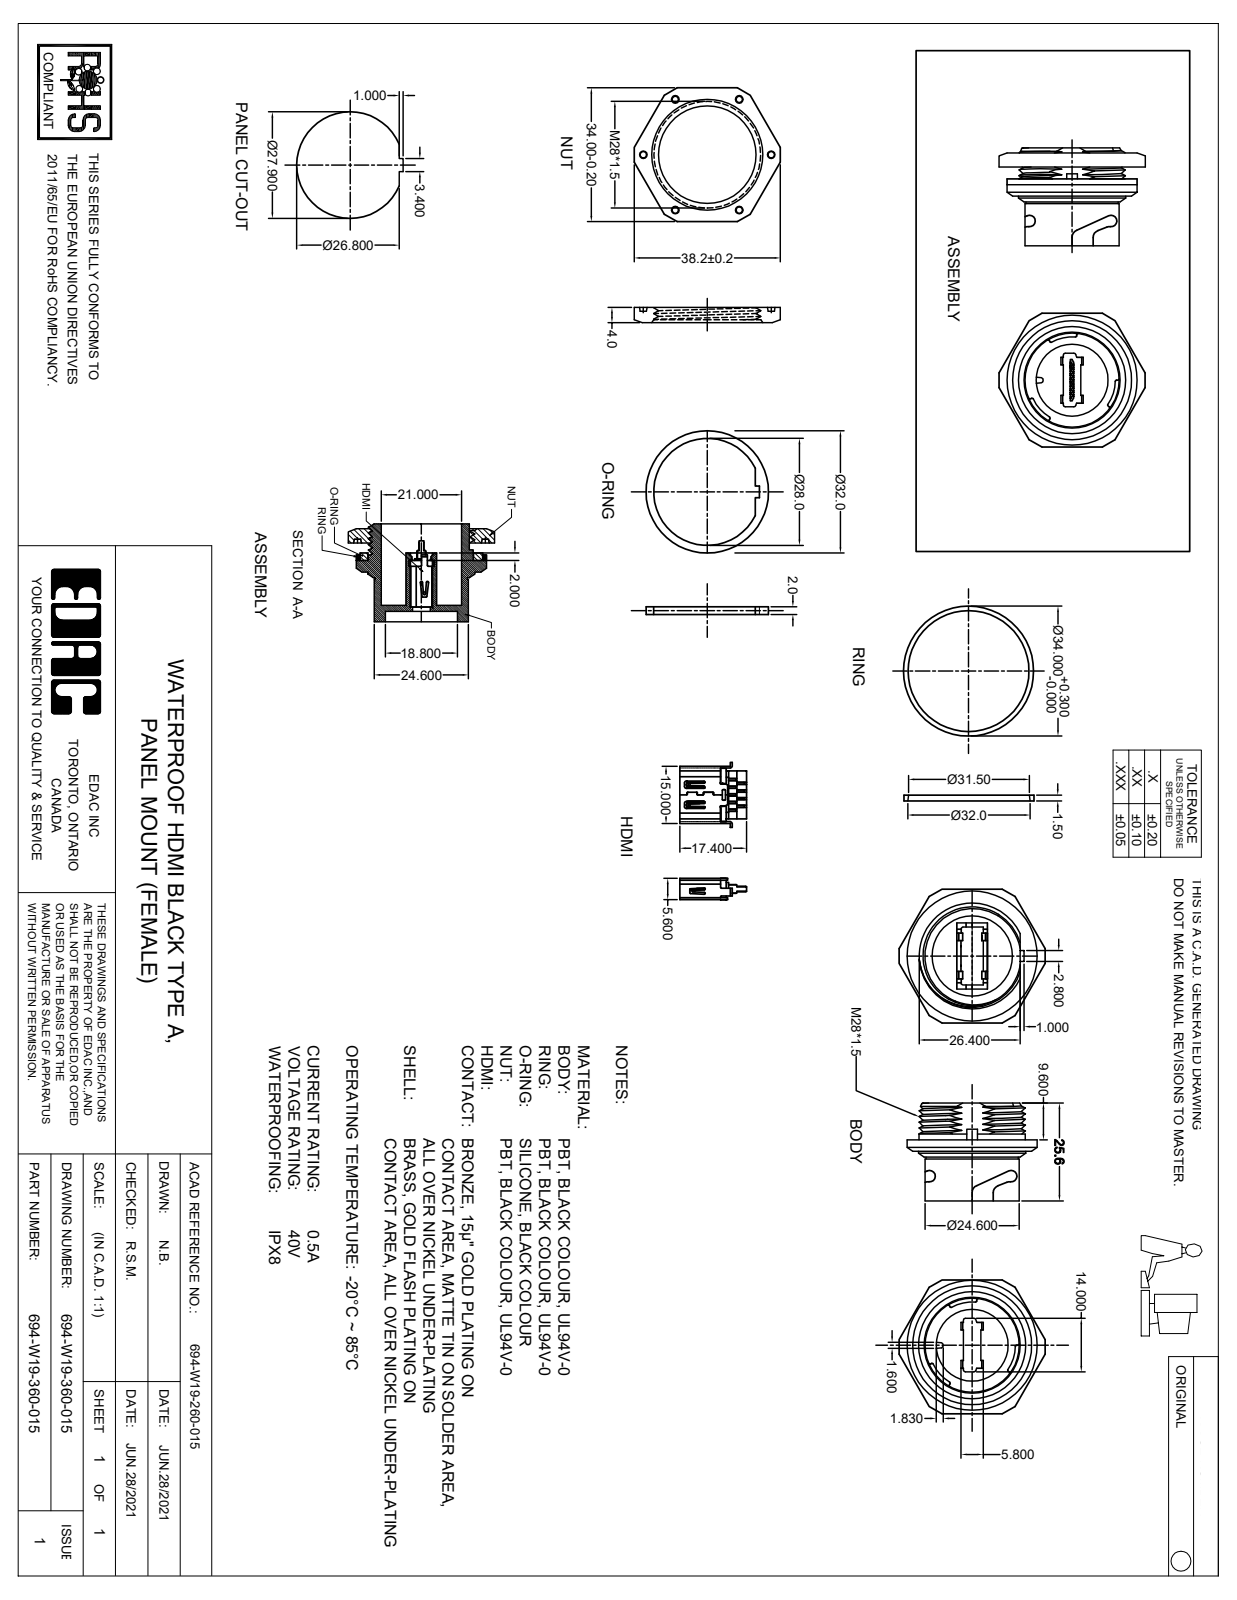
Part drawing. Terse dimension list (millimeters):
name: HDMI CONTACT2 694-W19-X60-015; HDMI ASSY 694-W19-X60-015; HOUSING 694-W19-X60-015; HDMI HOUSING2 694-W19-X60-015 (+7 more)
written by: SolidWorks 2020 (AUTOMOTIVE_DESIGN)
unit: mm
bodies: 26 solids, 2027 faces (1388 planar, 574 cylindrical, 65 other)
size: 38.2 × 34.77 × 25.6
volume: 9 559 mm³; area: 12 980 mm²
holes: 6× ⌀2, 1× ⌀18.8, 1× ⌀21, 1× ⌀26.25, 1× ⌀28
bosses: 1× ⌀34, 1× ⌀32, 1× ⌀27.8, 1× ⌀24.6, 1× ⌀24.1
rounds: 240× R0.15, 38× R0.21, 28× R0.2, 12× R0.5, 10× R0.25, 6× R0.1, 6× R0.35, 6× R0.65
face distances: 0.5, 4, 4.93, 1.1, 2.7, 8.93, 2, 6.93, 9.6, 5.68
hole spacings: 16.5, 28.58, 33, 16.51, 33.01
